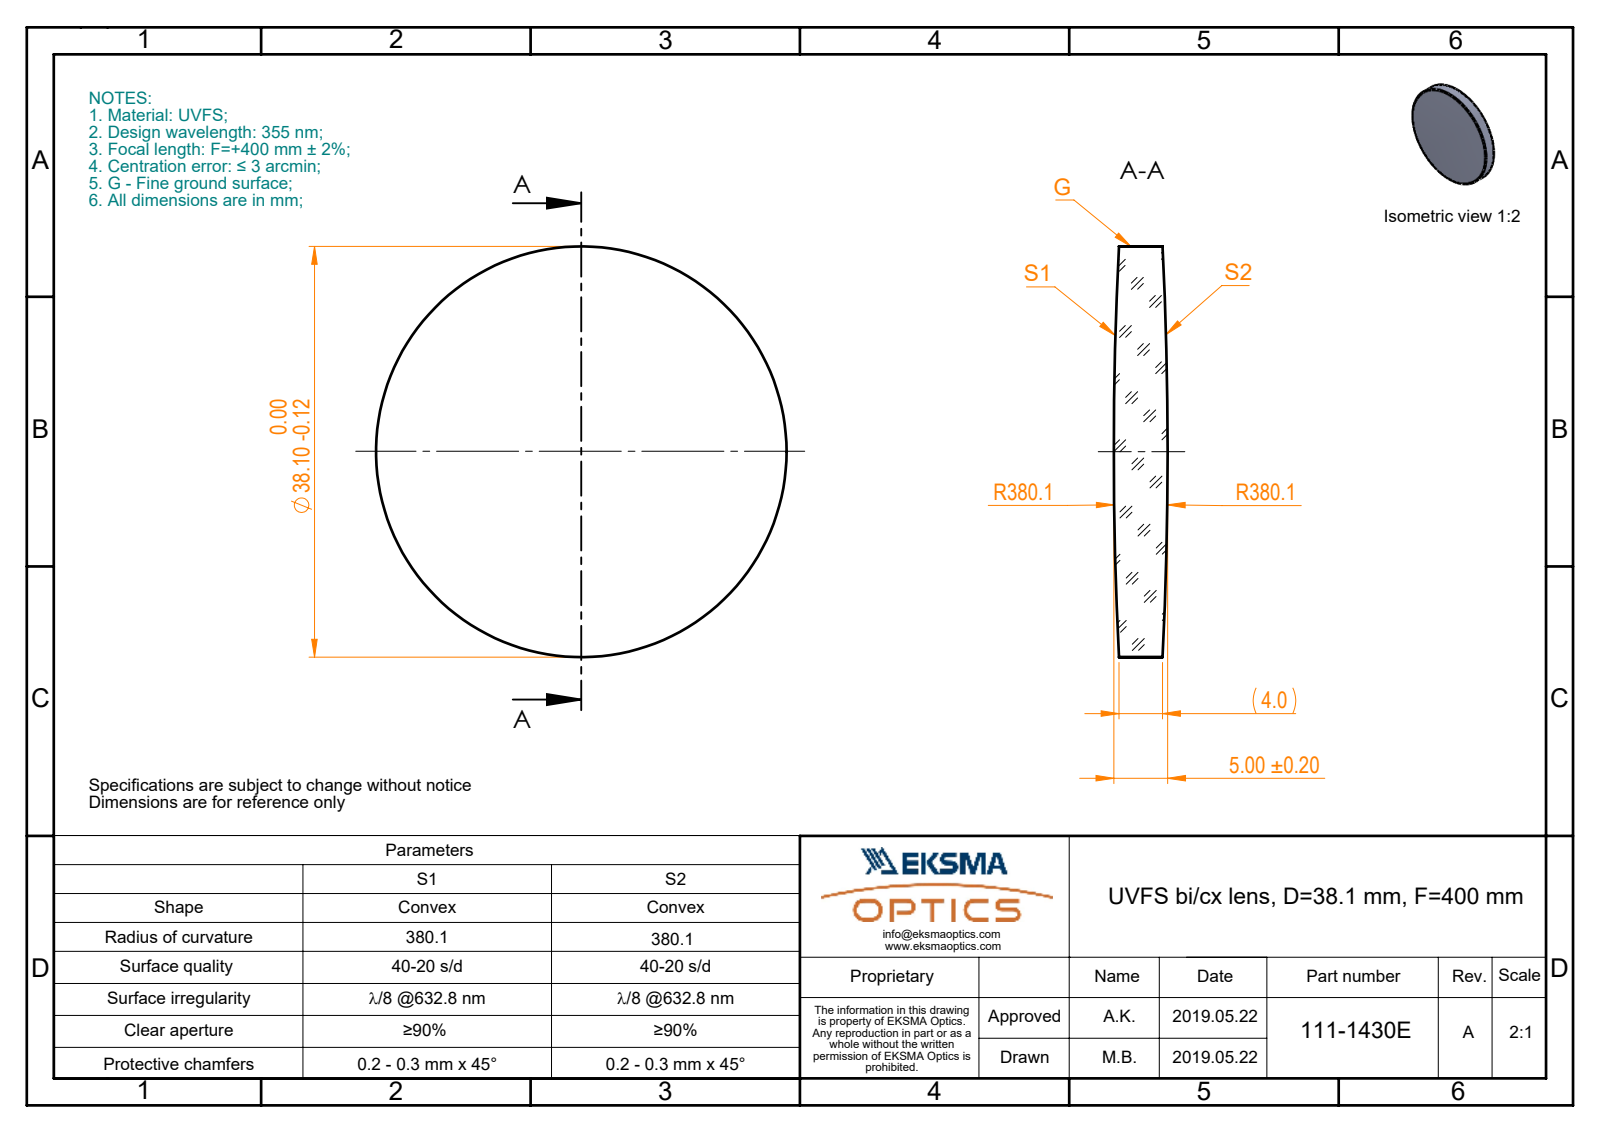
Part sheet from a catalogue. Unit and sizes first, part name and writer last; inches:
Units: inches
Overall size (bounding box): 1.5 × 1.5 × 0.197
Round bosses / shafts (diameter × count): ⌀1.5 ×1
Volume: 0.315 in³ · Surface area: 4.287 in²
Bodies: 1 solid, 6 faces (0 planar, 2 cylindrical, 4 other)
Part name (STEP PRODUCT): 111-1430E UVFS bi-cx 38.1 F400
STEP written by: SolidWorks 2017 (CONFIG_CONTROL_DESIGN)
